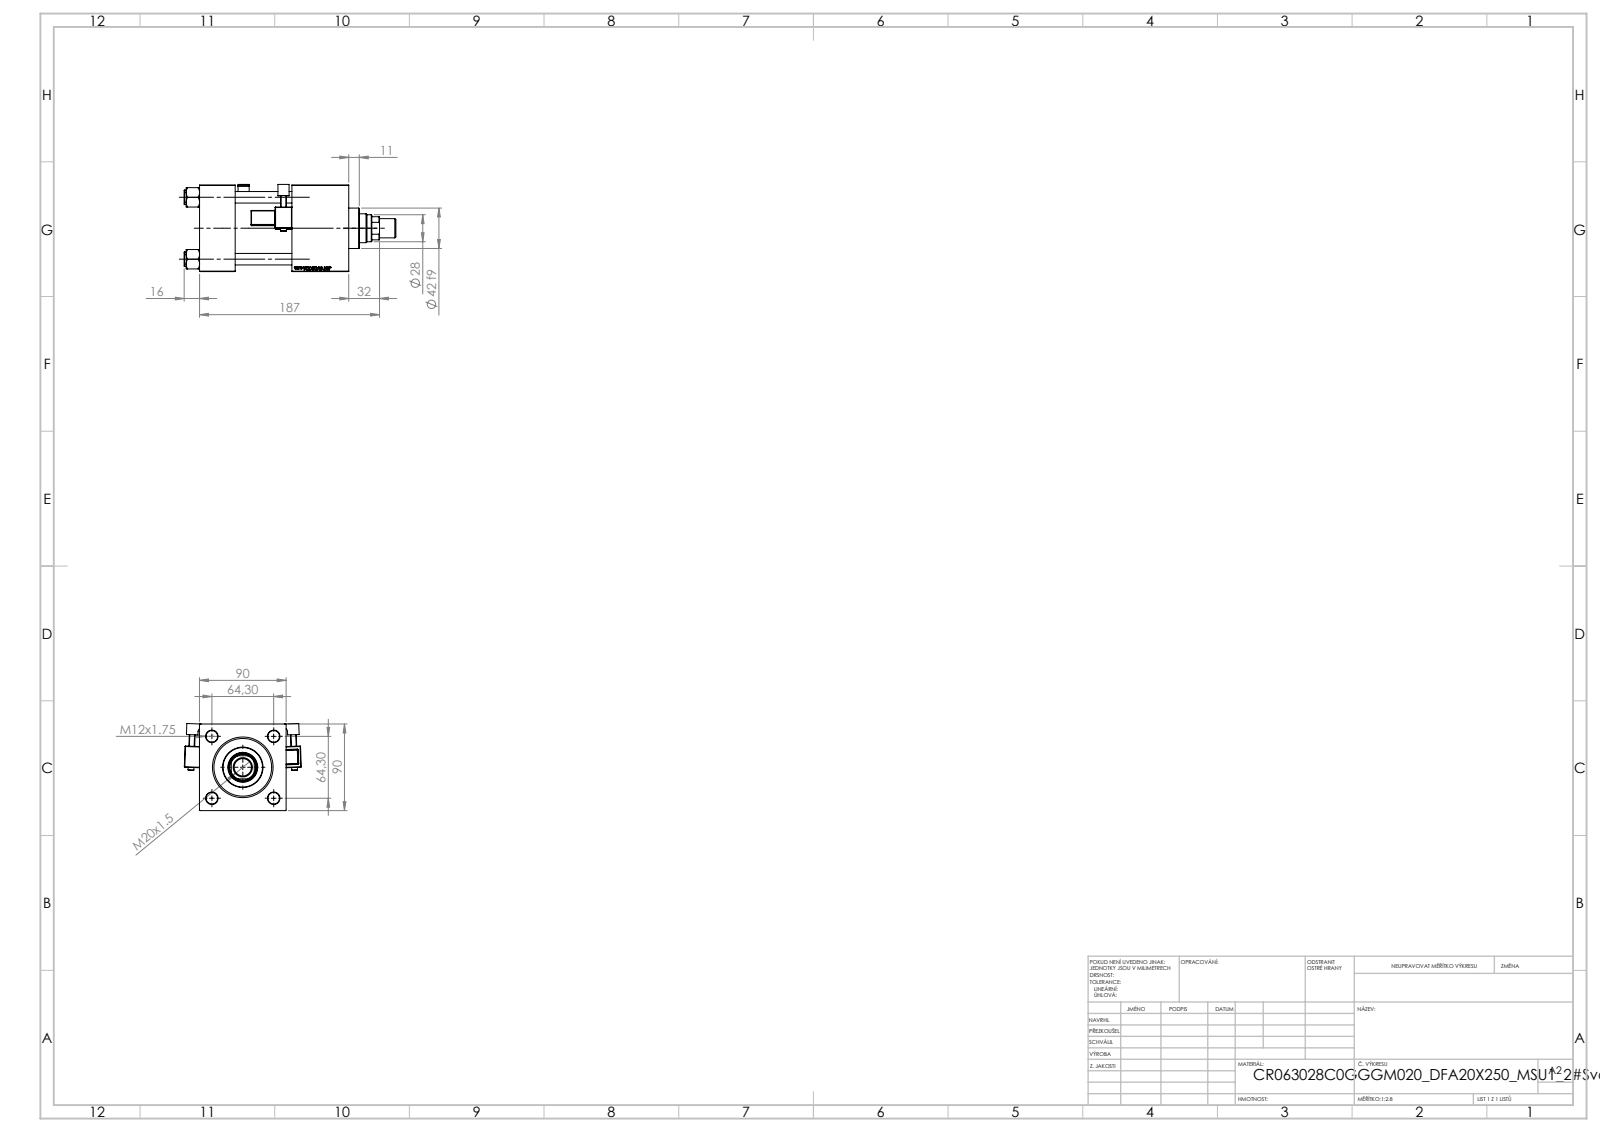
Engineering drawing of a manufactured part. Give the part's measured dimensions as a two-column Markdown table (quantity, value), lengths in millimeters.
| quantity | value |
| --- | --- |
| part name | NUT_M5_C; V215CR_MSU; V215CR_C_Body; V215_VC_A (+3 more) |
| STEP written by | SolidWorks 2019 (CONFIG_CONTROL_DESIGN) |
| units | millimeters |
| bodies | 14 solids, 1336 faces (596 planar, 156 cylindrical, 584 other) |
| overall size | 220 × 121.57 × 90.53 |
| volume | 1 012 000 mm³ |
| surface area | 199 056 mm² |
| round holes (diameter × count) | 12 × 4, 7 × 2, 20.96 × 2, 30 × 2, 18.5 × 1, 28 × 1, 31 × 1, 50 × 1, 60 × 1, 63 × 1 |
| round bosses / shafts (diameter × count) | 15 × 4, 6 × 2, 69 × 1, 42 × 1, 36 × 1, 30 × 1, 20 × 1, 18 × 1 |
| partial cylindrical surfaces (radius × count) | 0.5 × 48, 1 × 2, 2.5 × 2, 4 × 2, 7.5 × 1, 12 × 1, 13.5 × 1 |
| main face-to-face distances | 90, 59, 37, 155, 118, 96, 126.3, 89.3, 30.3, 28.7 |
| hole center spacings | 45.47, 64.3, 90.93, 97.5 |
